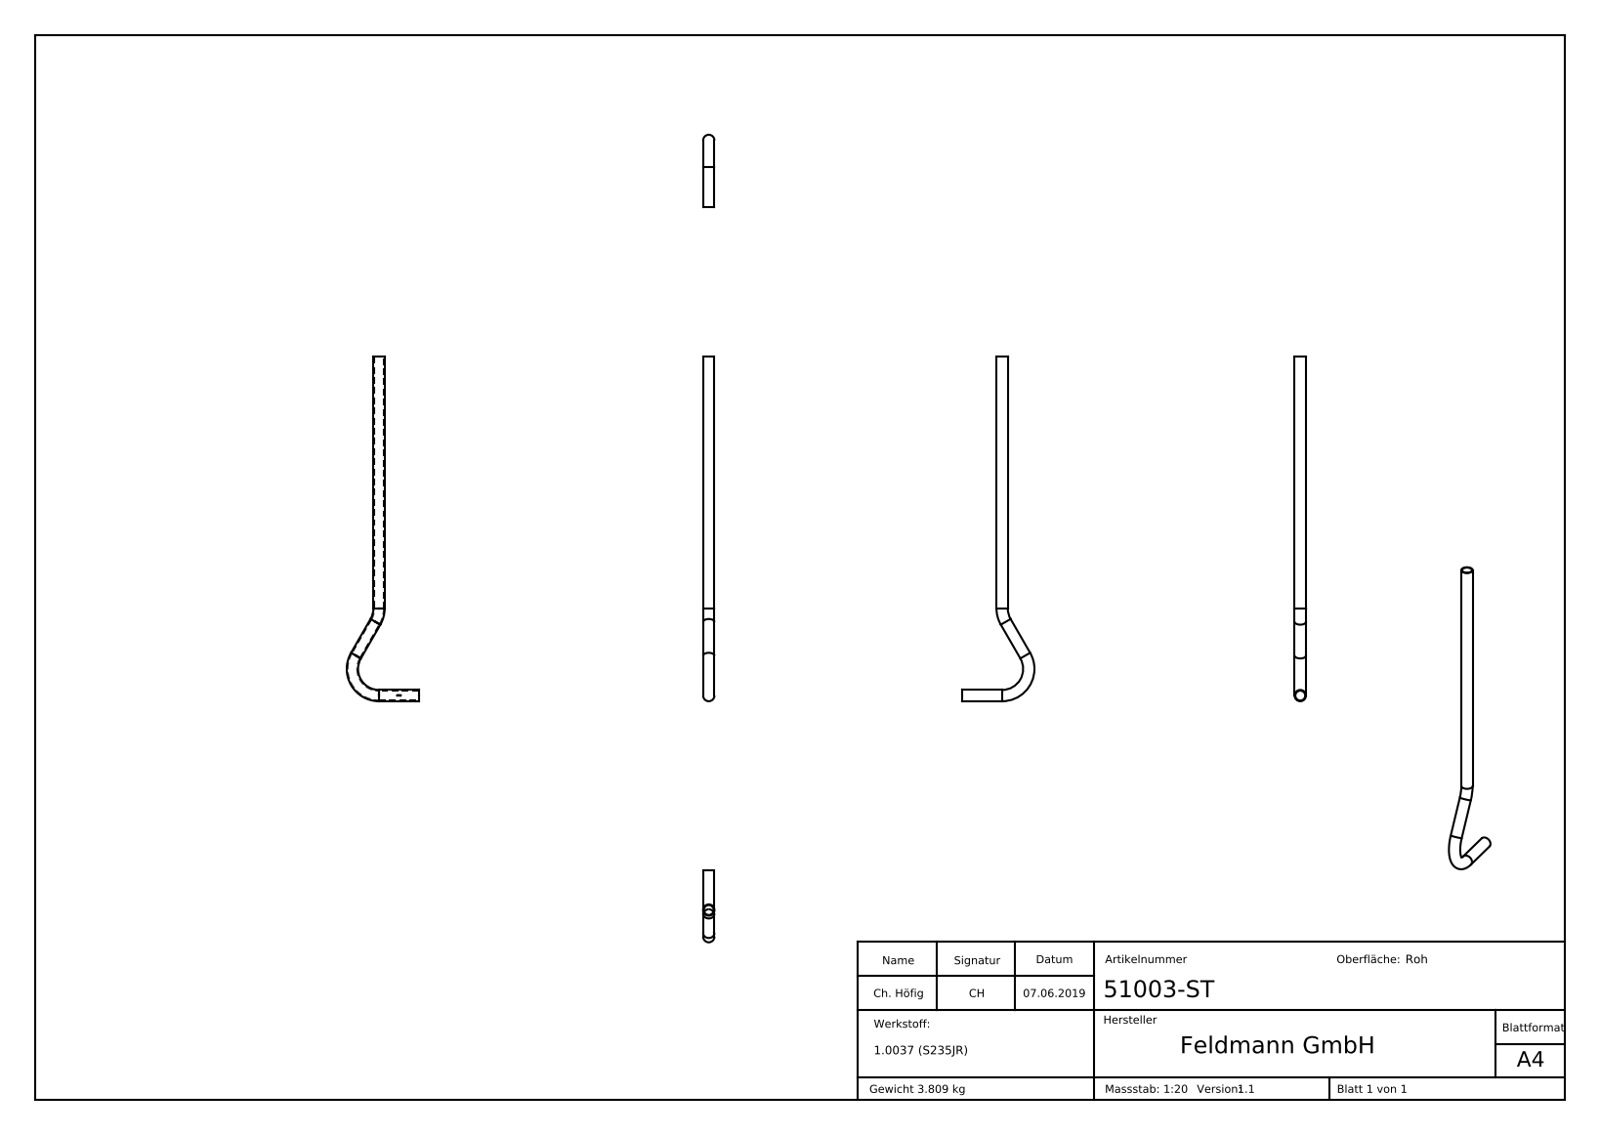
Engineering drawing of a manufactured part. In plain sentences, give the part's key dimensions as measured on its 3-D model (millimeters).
The part is named "51003-ST". Its 3-D file was written by "SolidWorks 2015 (CONFIG_CONTROL_DESIGN)". It is 1 solid with 233 faces: 85 planar, 33 cylindrical and 115 other. Overall it measures 1292.99 by 270 by 42.4 millimeters. Its volume is 488 289 cubic millimeters and its surface area 376 266 square millimeters. Round holes: 3 of diameter 37.2. Round bosses or shafts: 3 of diameter 42.4. Partial cylindrical surfaces (rounded edges, fillets, slot ends): 1 of radius 18.7. The main face-to-face distances are 2.97, 0.39, 5.73, 8.7, 2.02, 10.72, 1270.47, 1.32, 4.09, 4.36.
